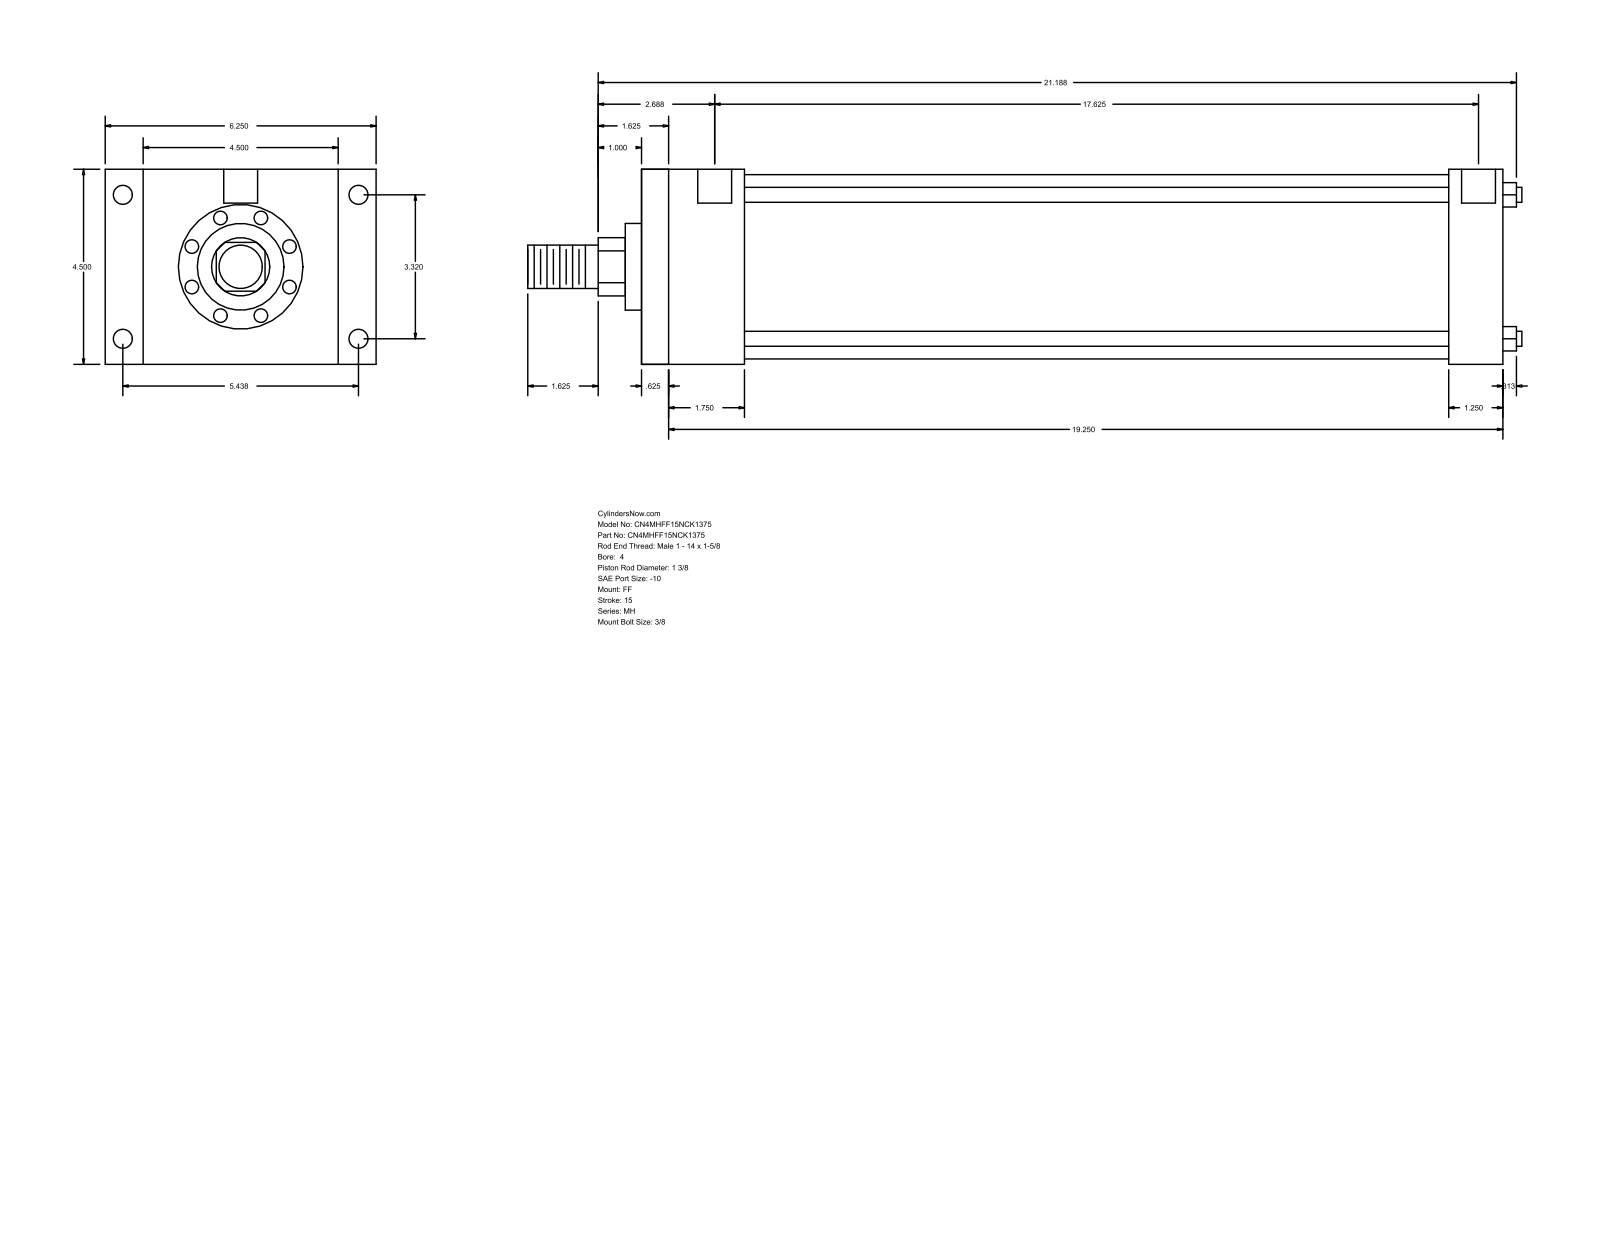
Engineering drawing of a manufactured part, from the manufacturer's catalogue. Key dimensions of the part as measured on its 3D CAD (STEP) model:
Part name (STEP PRODUCT): MH_FF__0400_1.375
STEP written by: GSSL Pune (CONFIG_CONTROL_DESIGN)
Units: millimetres
Bodies: 0 solids, 92 faces (64 planar, 28 cylindrical, 0 other)
Overall size (bounding box): 582.61 × 158.75 × 114.3
Round holes (diameter × count): ⌀8.73 ×4, ⌀11.13 ×4, ⌀19.84 ×2
Round bosses / shafts (diameter × count): ⌀8.76 ×4, ⌀107.95 ×1, ⌀50.8 ×1, ⌀34.92 ×1, ⌀25.4 ×1
Partial cylindrical surfaces — rounded edges, fillets, slot ends (radius × count): R17.06 ×1
Main face-to-face distances: 114.3, 504.83, 15.87, 488.96, 60.32, 44.45, 444.51, 473.08, 457.21, 412.76
Hole centre spacings: 84.32, 138.12, 161.82, 450.85, 1.58, 1.59, 447.68, 449.26
